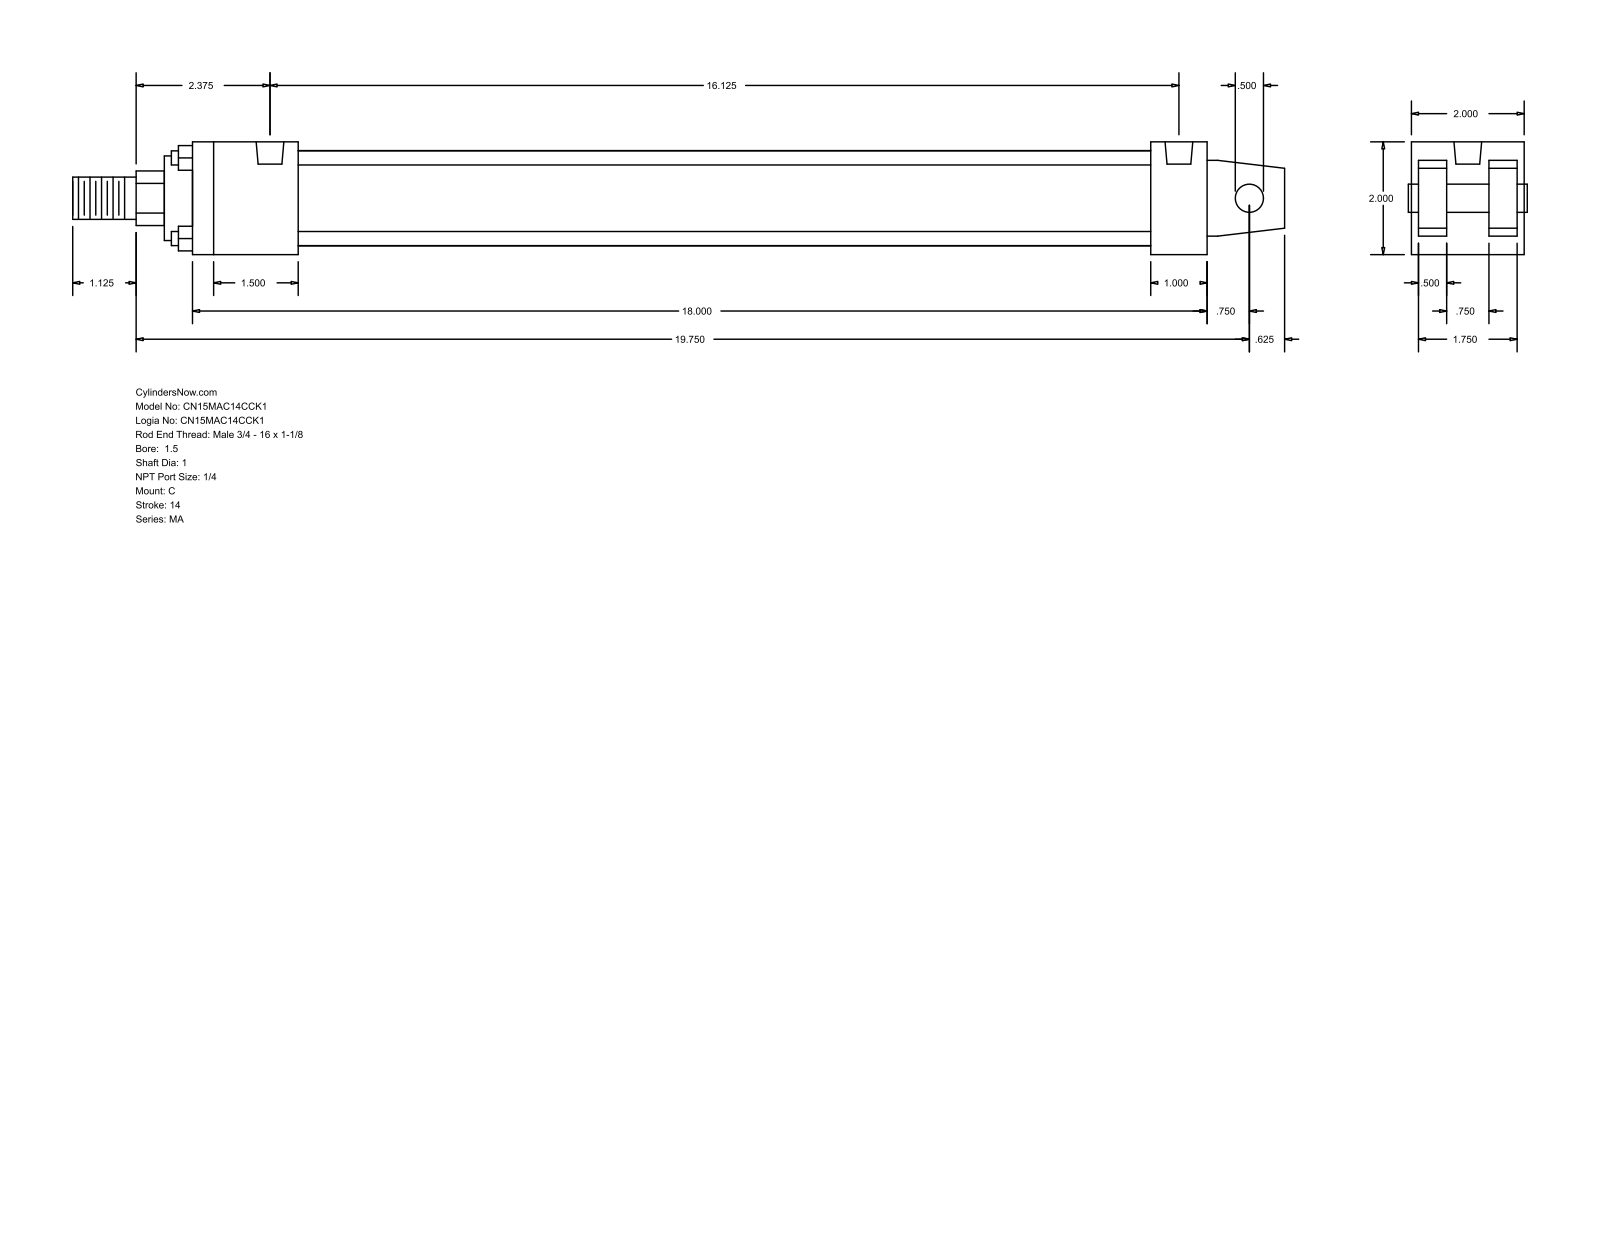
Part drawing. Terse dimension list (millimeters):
name: MA_C__0150_1
written by: GSSL Pune (CONFIG_CONTROL_DESIGN)
unit: mm
bodies: 0 solids, 103 faces (76 planar, 27 cylindrical, 0 other)
size: 546.1 × 50.8 × 50.8
holes: 4× ⌀7.94, 2× ⌀12.49
bosses: 4× ⌀6.35, 1× ⌀42.93, 1× ⌀38.1, 1× ⌀25.4, 1× ⌀19.05, 1× ⌀12.7
rounds: 1× R12.29
face distances: 50.8, 47.63, 12.7, 3.17, 15.87, 34.93, 31.76, 457.2, 25.4, 431.8
hole spacings: 409.57
